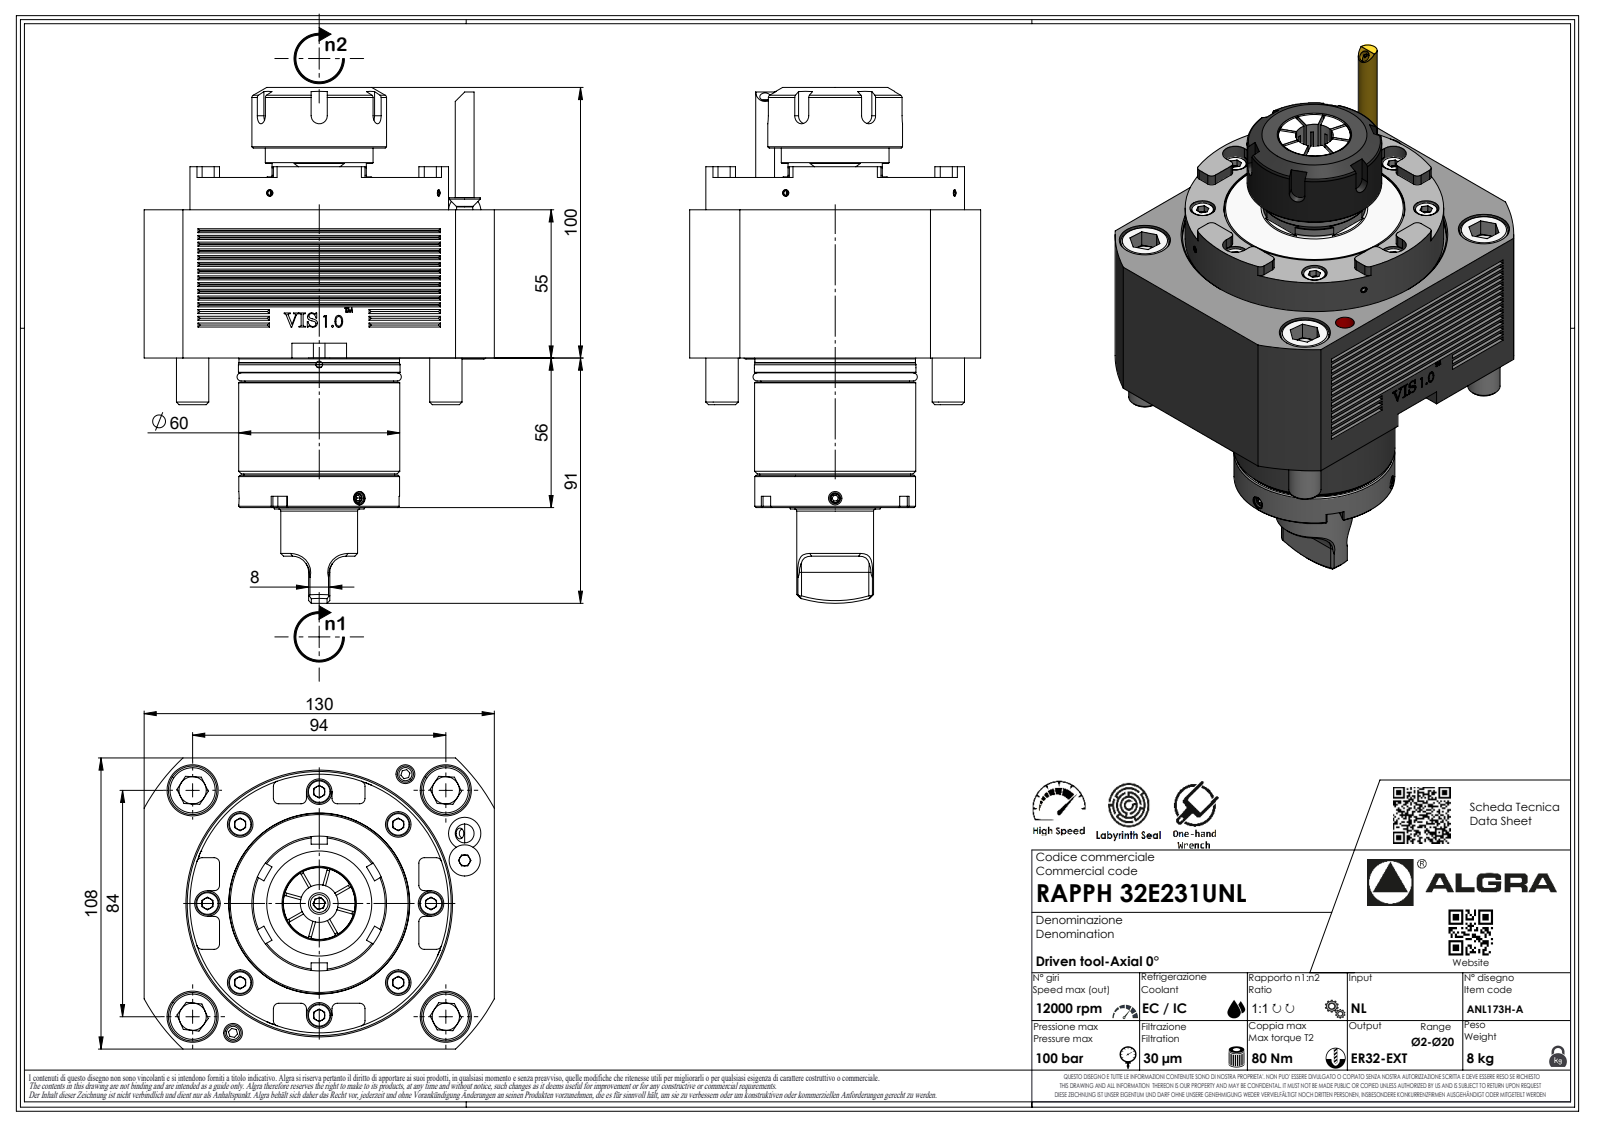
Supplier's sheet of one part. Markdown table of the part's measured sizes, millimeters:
| quantity | value |
| --- | --- |
| part name | RAPPH32E231UNL |
| STEP written by | SolidWorks 2023 (AUTOMOTIVE_DESIGN) |
| units | millimeters |
| bodies | 1 solid, 490 faces (296 planar, 85 cylindrical, 109 other) |
| overall size | 191.41 × 130 × 108 |
| volume | 1 065 000 mm³ |
| surface area | 76 941 mm² |
| round holes (diameter × count) | 2.1 × 1, 4 × 1 |
| round bosses / shafts (diameter × count) | 96 × 1, 60 × 1, 59.8 × 1, 50 × 1, 40 × 1, 28.5 × 1, 7 × 1, 6.37 × 1 |
| partial cylindrical surfaces (radius × count) | 2 × 25, 0.33 × 7, 0.52 × 7, 3.7 × 7, 6 × 6, 4.75 × 4, 3 × 3, 0.21 × 1 |
| main face-to-face distances | 55, 108, 67, 12, 130, 55.5, 110.5, 122.5, 155.91, 100.41 |
